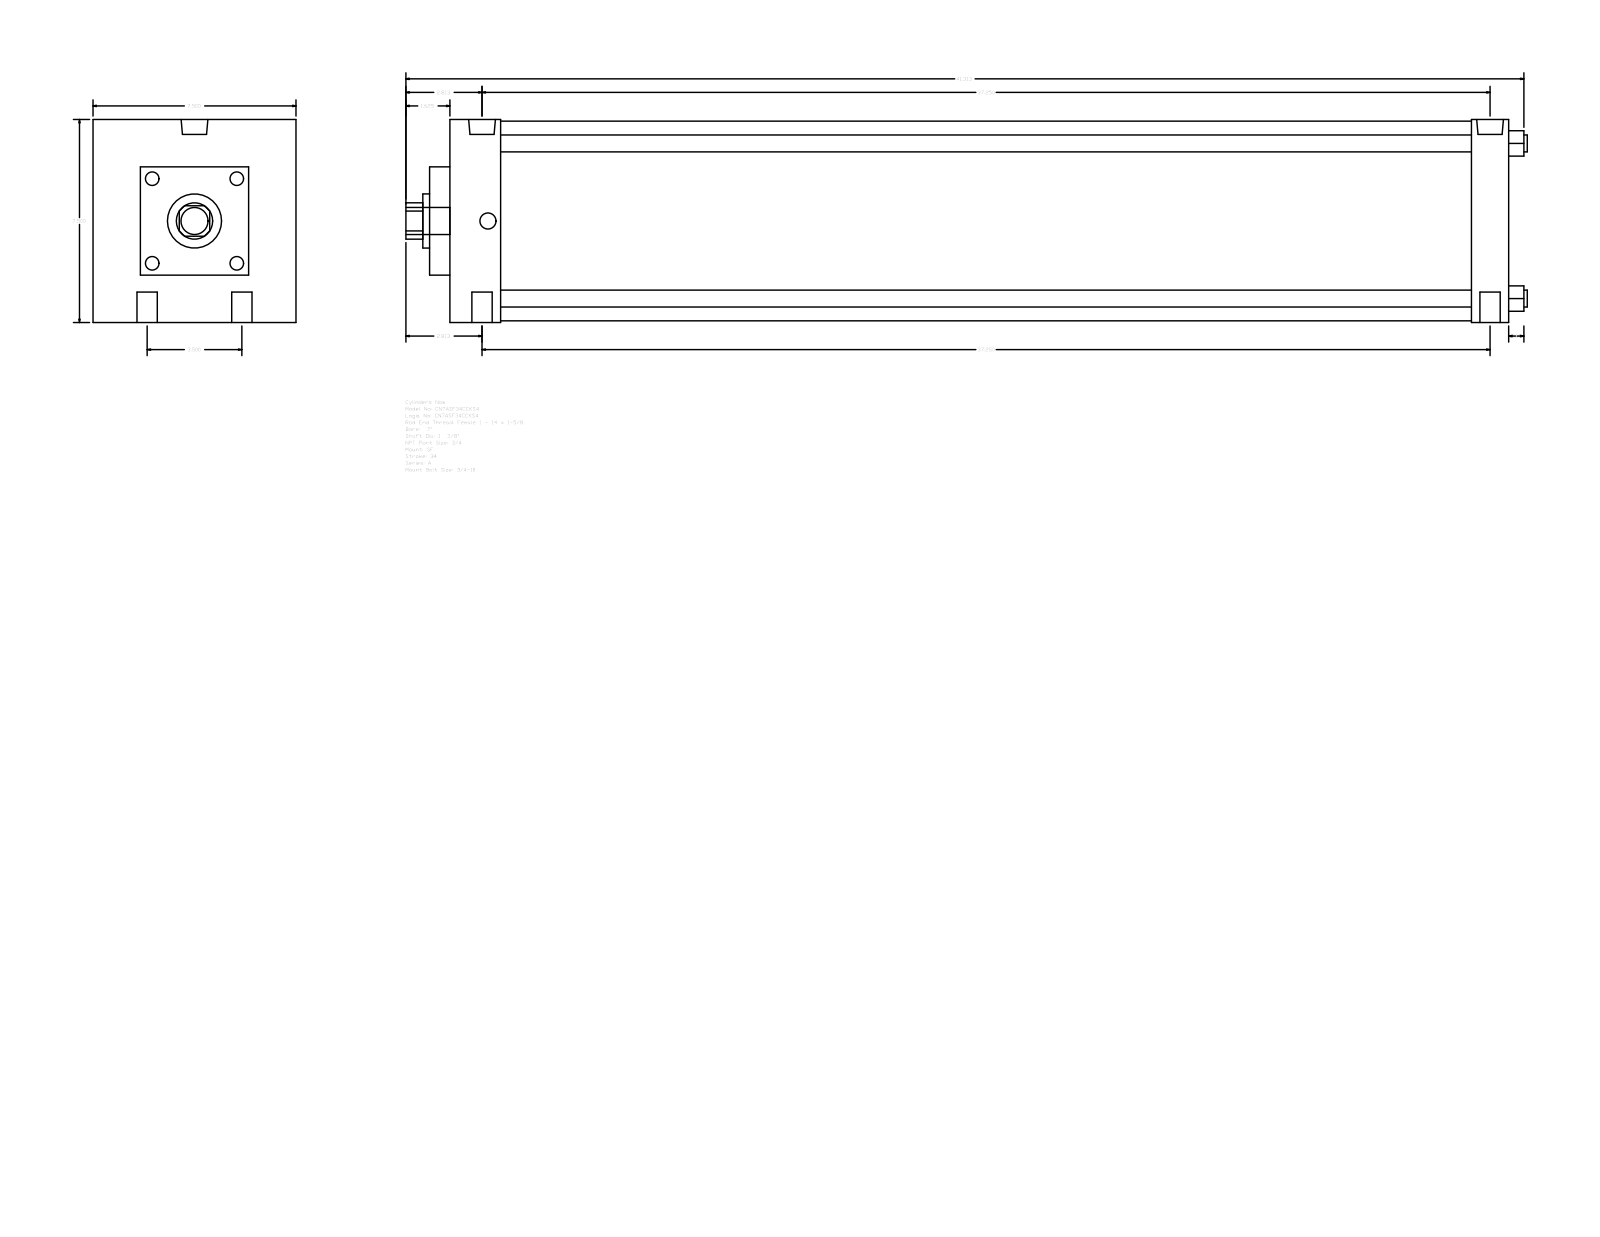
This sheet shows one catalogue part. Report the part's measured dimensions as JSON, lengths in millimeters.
{"part_name": "A_SF__0700_1.375", "step_written_by": "GSSL Pune (CONFIG_CONTROL_DESIGN)", "units": "millimeters", "bodies": {"solids": 0, "faces": 93, "planar": 67, "cylindrical": 26, "other": 0}, "overall_size": [1052.51, 190.5, 190.5], "round_holes": [[19.05, 4], [15.08, 2], [25.12, 2], [34.92, 1], [50.8, 1]], "round_bosses_or_shafts": [[15.88, 4], [187.32, 1], [25.4, 1]], "partial_cylinders_radius": [[17.06, 1]], "face_to_face_distances": [190.5, 993.78, 19.04, 1012.82, 66.67, 977.89, 47.63, 958.85, 911.22, 946.15], "hole_center_spacings": [44.45, 947.19, 946.15, 88.9, 950.32, 935.03]}
